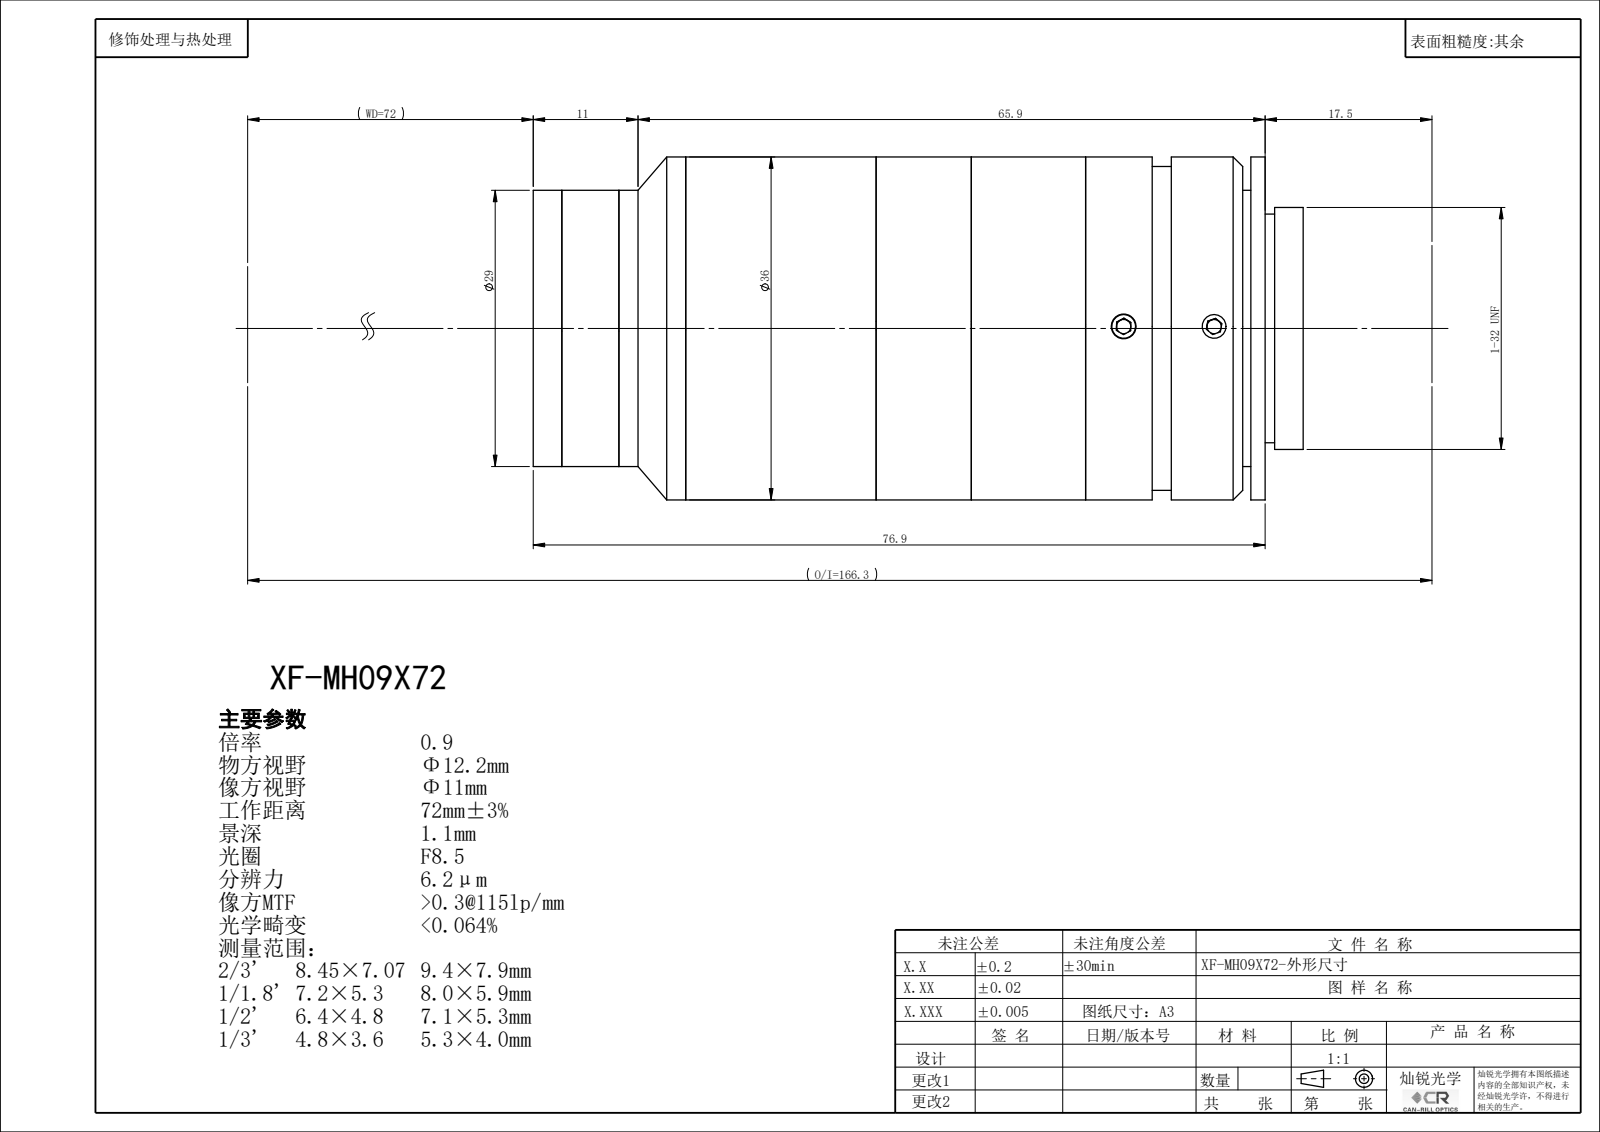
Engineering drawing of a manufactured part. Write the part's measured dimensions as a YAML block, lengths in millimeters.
part_name: "XF-MH09X72"
step_written_by: "SolidWorks 2022 (CONFIG_CONTROL_DESIGN)"
units: millimeters
bodies: {solids: 0, faces: 137, planar: 71, cylindrical: 44, other: 22}
overall_size: [80.87, 36.01, 36]
round_holes:
  - {diameter: 2.5, count: 3}
  - {diameter: 14, count: 1}
  - {diameter: 22.4, count: 1}
  - {diameter: 24, count: 1}
  - {diameter: 24.9, count: 1}
  - {diameter: 26.4, count: 1}
  - {diameter: 27, count: 1}
round_bosses_or_shafts:
  - {diameter: 36, count: 1}
  - {diameter: 34, count: 1}
  - {diameter: 29, count: 1}
  - {diameter: 25.4, count: 1}
face_to_face_distances: [18.85, 54.22, 73.07, 1.5, 71.57, 17.35, 42.22, 12, 29.35, 30.85]
